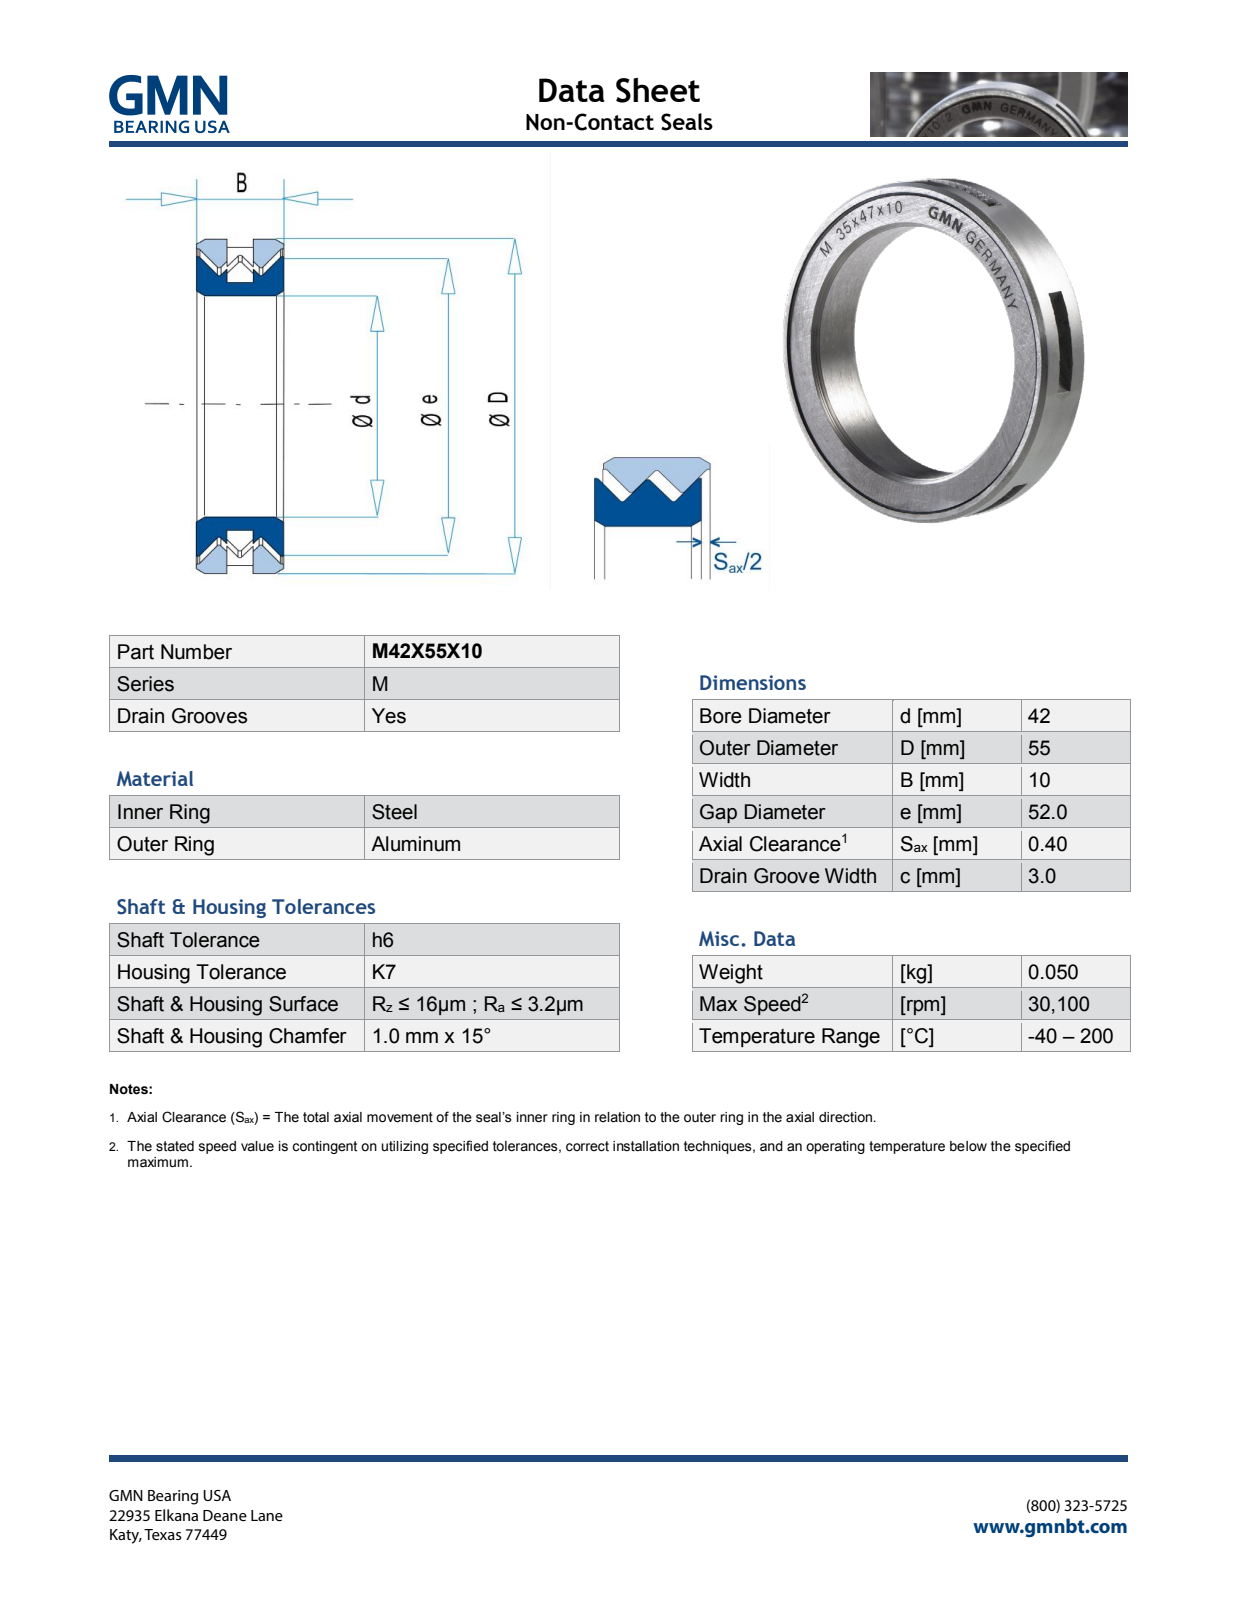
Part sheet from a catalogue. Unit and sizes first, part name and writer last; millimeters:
Units: millimetres
Overall size (bounding box): 55 × 55 × 10.07
Round holes (diameter × count): ⌀42 ×1, ⌀52.28 ×1
Round bosses / shafts (diameter × count): ⌀55 ×1, ⌀52 ×1
Partial cylindrical surfaces — rounded edges, fillets, slot ends (radius × count): R10 ×5
Main face-to-face distances: 10, 3.5, 6.5, 3, 3.57, 6.57, 10.07, 2.42, 2.12, 0.31
Volume: 8 652 mm³ · Surface area: 8 997 mm²
Bodies: 2 solids, 596 faces (519 planar, 27 cylindrical, 50 other)
Part name (STEP PRODUCT): M42X55X10_PRT
STEP written by: PRO/ENGINEER BY PARAMETRIC TECHNOLOGY CORPORATION, 2013150 (AUTOMOTIVE_DESIGN)
